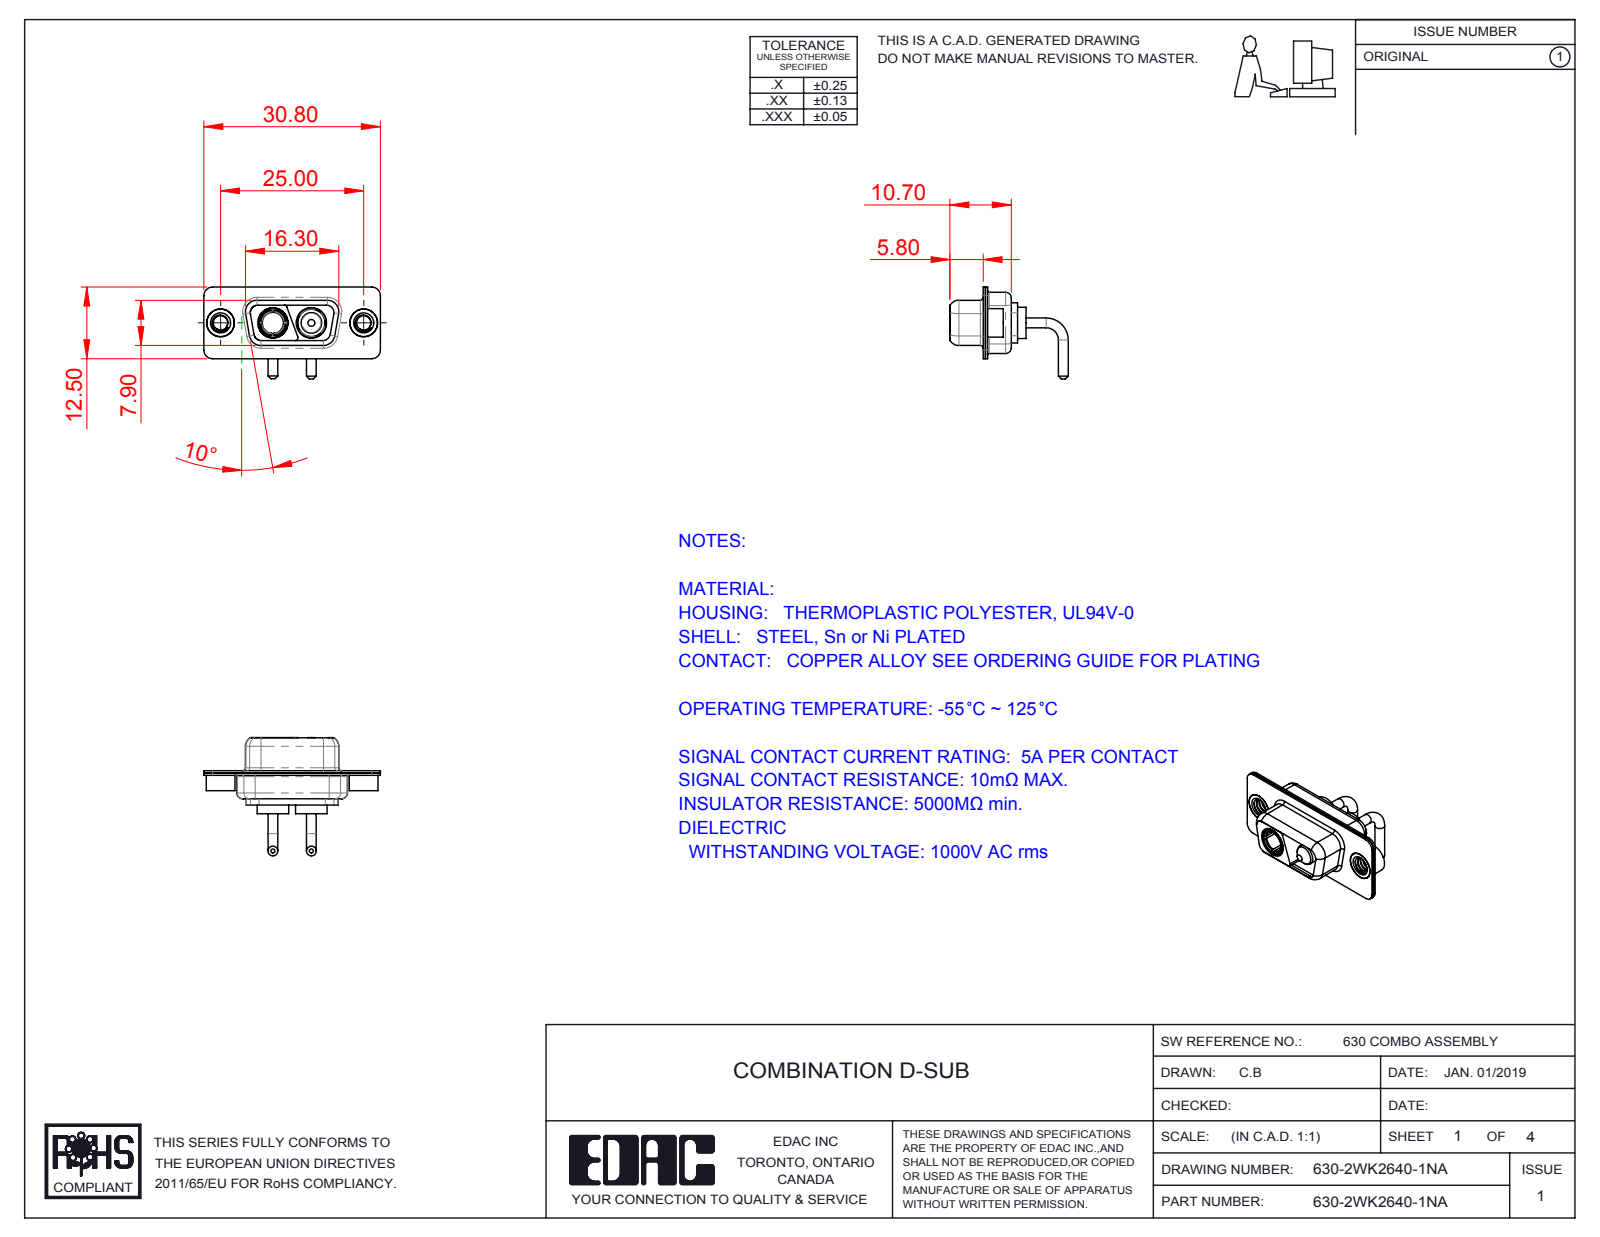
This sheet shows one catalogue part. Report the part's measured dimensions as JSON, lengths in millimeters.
{"part_name": "630Combo Shell Rear_09 Contacts; 630Combo Threaded Rivet_A; 630Combo Housing_2WK2; 630Combo Shell Front_09 Contacts (+3 more)", "step_written_by": "SolidWorks 2020 (CONFIG_CONTROL_DESIGN)", "units": "millimeters", "bodies": {"solids": 9, "faces": 395, "planar": 106, "cylindrical": 182, "other": 107}, "overall_size": [30.8, 20.65, 16.05], "volume_mm3": 1575, "surface_area_mm2": 4003, "round_holes": [[4.85, 4], [2.5, 2], [4, 2], [4.05, 2], [5.3, 2], [3.7, 1]], "round_bosses_or_shafts": [[1.7, 4], [5.5, 2], [5.2, 2], [5, 2], [4.95, 2], [4.8, 2], [4.75, 2], [3.75, 2]], "partial_cylinders_radius": [[1.5, 16], [2, 12], [1.35, 8], [1.6, 8], [0.5, 6], [0.25, 4], [0.6, 4], [0.65, 4]], "face_to_face_distances": [0.4, 1.4, 0.8, 8.45, 0.45, 8.9, 1.8, 7.5, 1, 7.05], "hole_center_spacings": [9.14, 15.86, 6.72, 25]}
